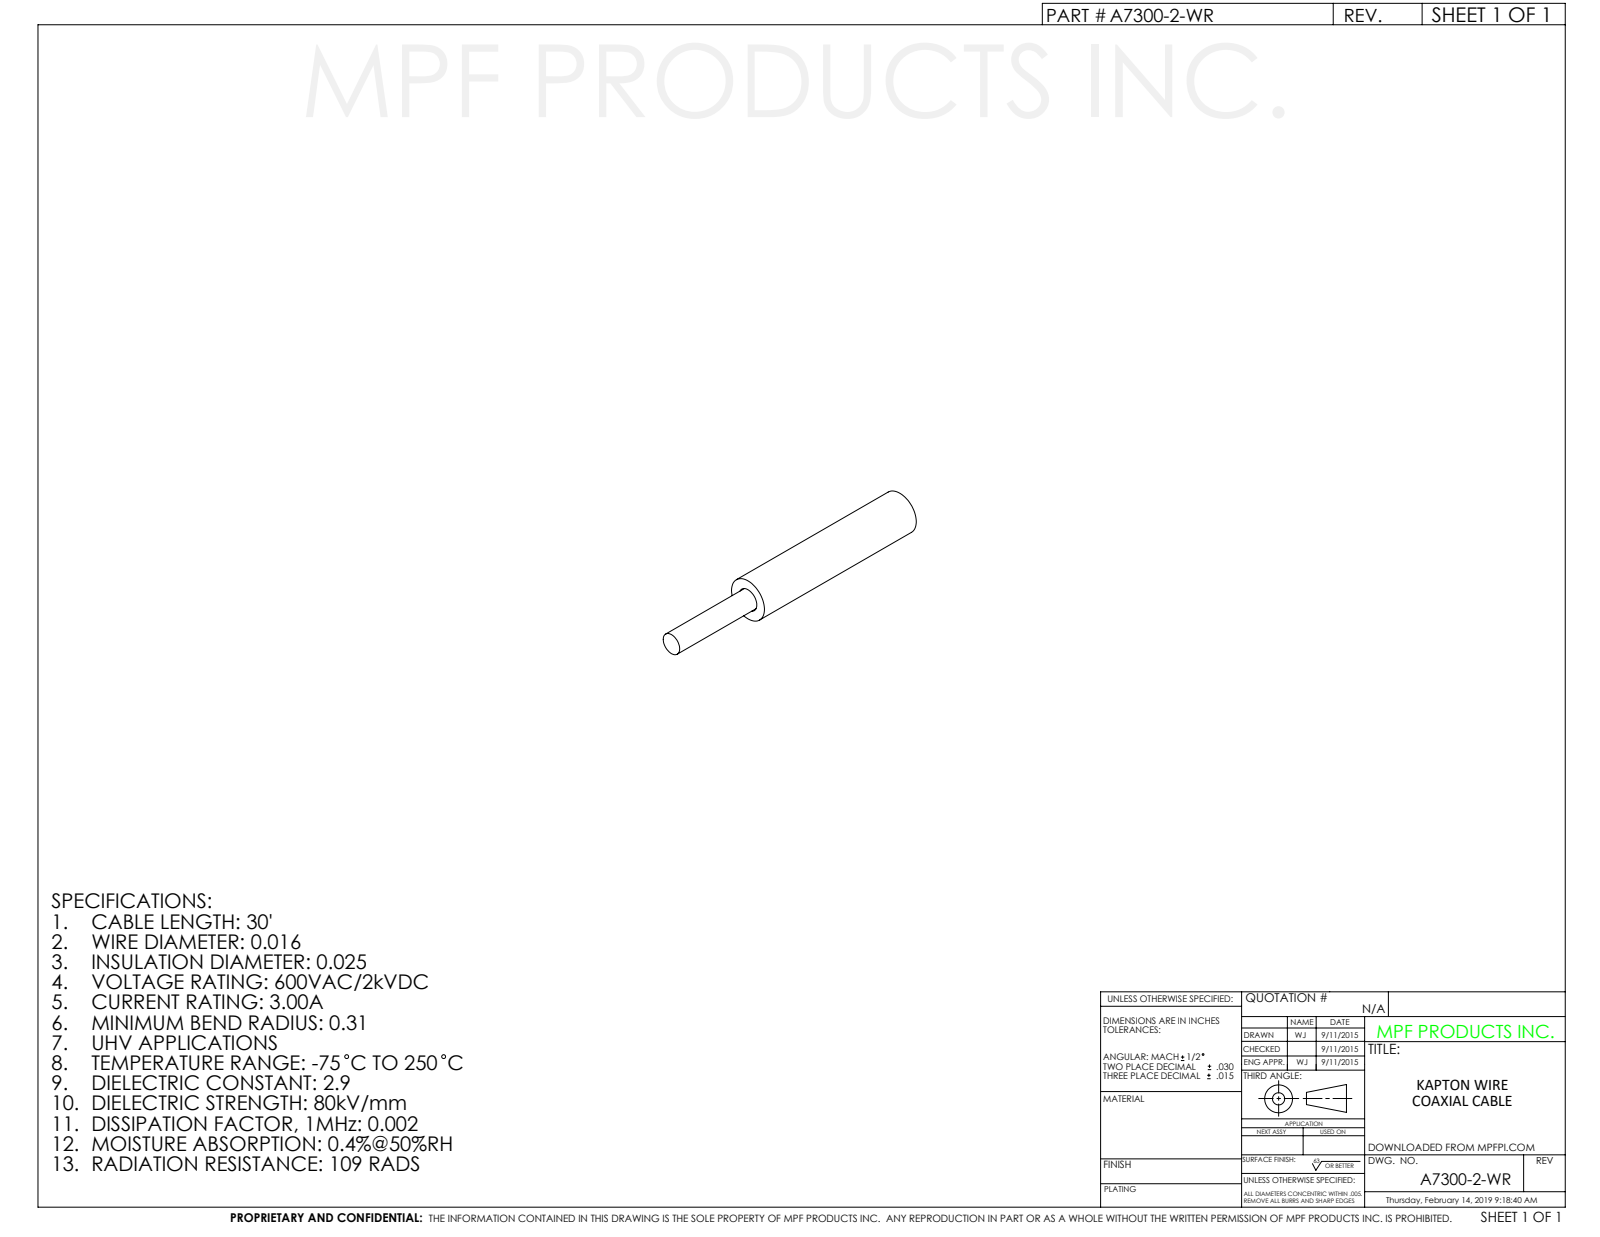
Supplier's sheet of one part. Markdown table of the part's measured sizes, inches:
| quantity | value |
| --- | --- |
| part name | A7300-2-WR |
| STEP written by | SolidWorks 2012 (CONFIG_CONTROL_DESIGN) |
| units | inches |
| bodies | 2 solids, 11 faces (3 planar, 6 cylindrical, 2 other) |
| overall size | 0.14 × 0.02 × 0.02 |
| round holes (diameter × count) | 0.011 × 1 |
| round bosses / shafts (diameter × count) | 0.02 × 1, 0.01 × 1 |
| main face-to-face distances | 0.092 |
